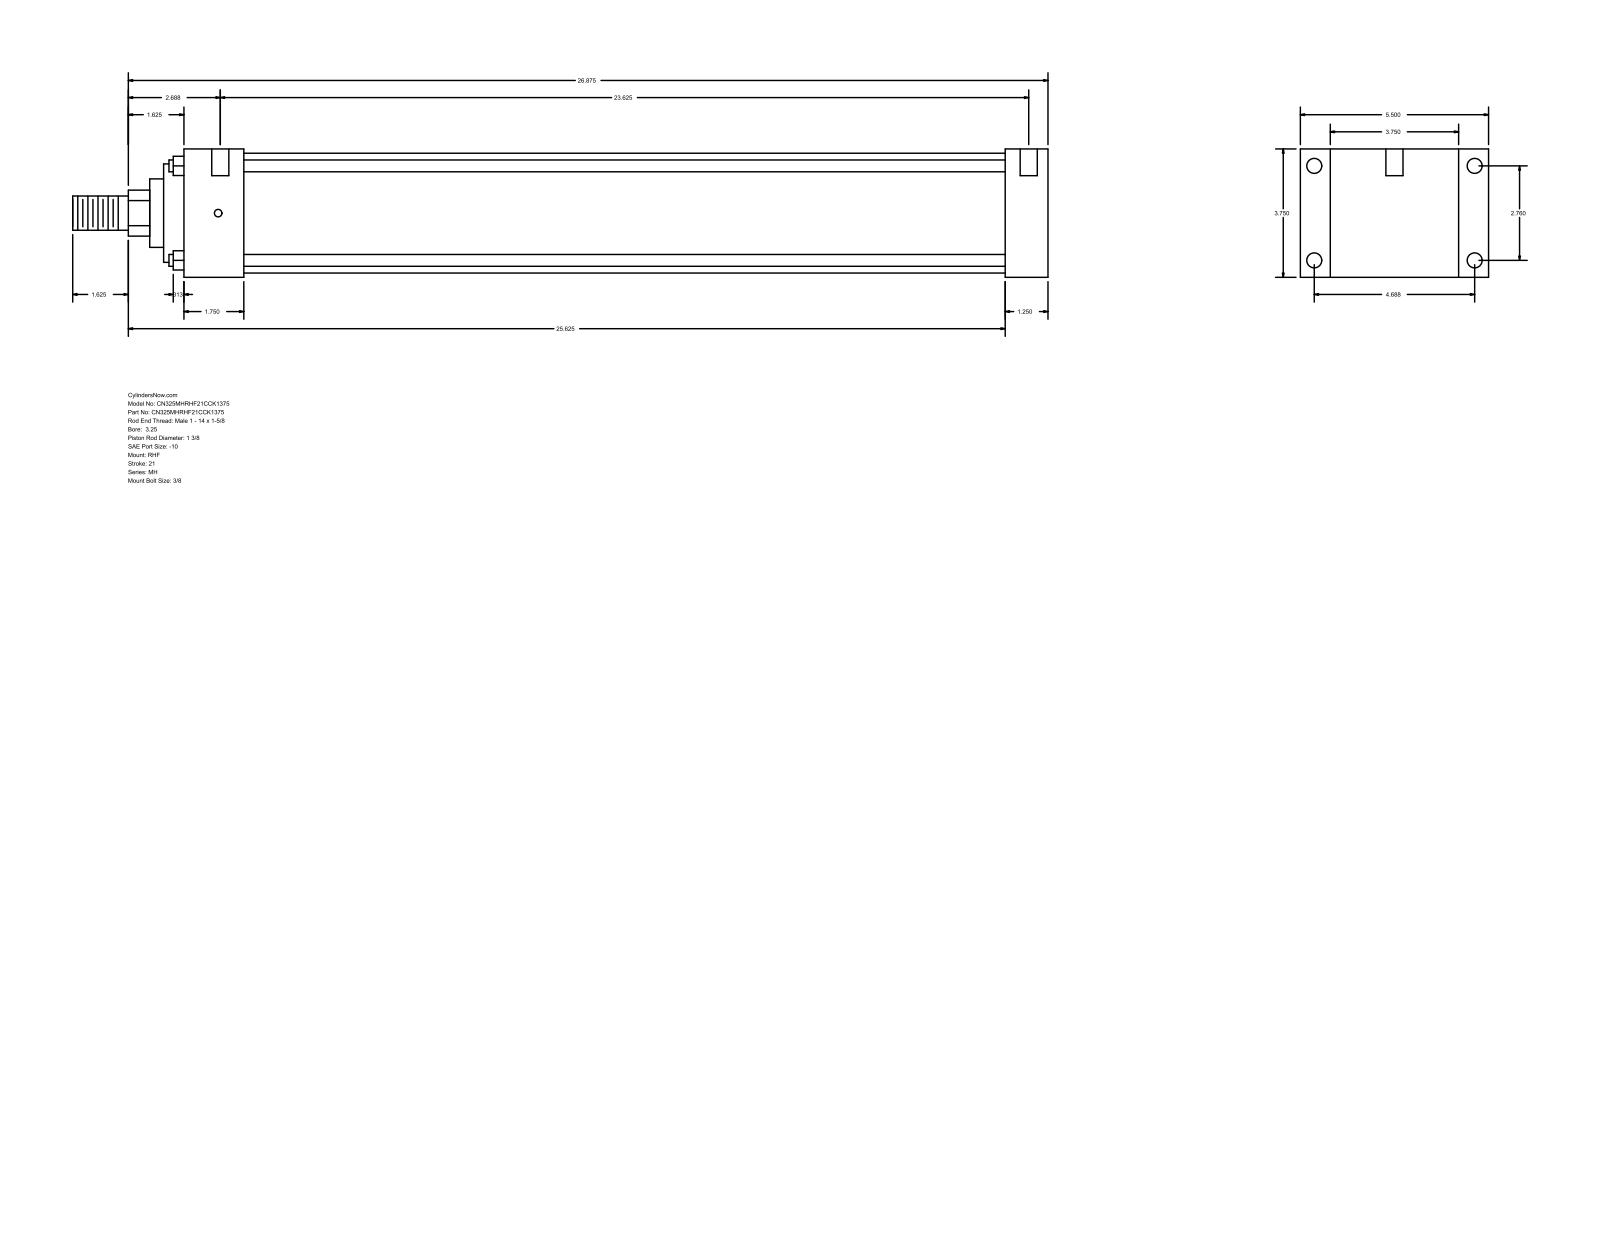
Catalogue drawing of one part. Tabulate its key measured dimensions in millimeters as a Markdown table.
| quantity | value |
| --- | --- |
| part name | MH_RHF__0325_1.375 |
| STEP written by | GSSL Pune (CONFIG_CONTROL_DESIGN) |
| units | millimeters |
| bodies | 0 solids, 90 faces (61 planar, 29 cylindrical, 0 other) |
| overall size | 723.9 × 139.7 × 95.25 |
| round holes (diameter × count) | 5.56 × 4, 11.13 × 4, 12.7 × 2 |
| round bosses / shafts (diameter × count) | 8.76 × 4, 88.9 × 1, 73.03 × 1, 50.8 × 1, 34.92 × 1, 25.4 × 1 |
| partial cylindrical surfaces (radius × count) | 17.06 × 1 |
| main face-to-face distances | 95.24, 31.74, 22.23, 117.47, 609.61, 641.35, 139.7, 44.45, 565.16, 596.9 |
| hole center spacings | 70.1, 119.06, 138.16, 606.43, 1.59, 4.76, 600.08, 601.67 |
